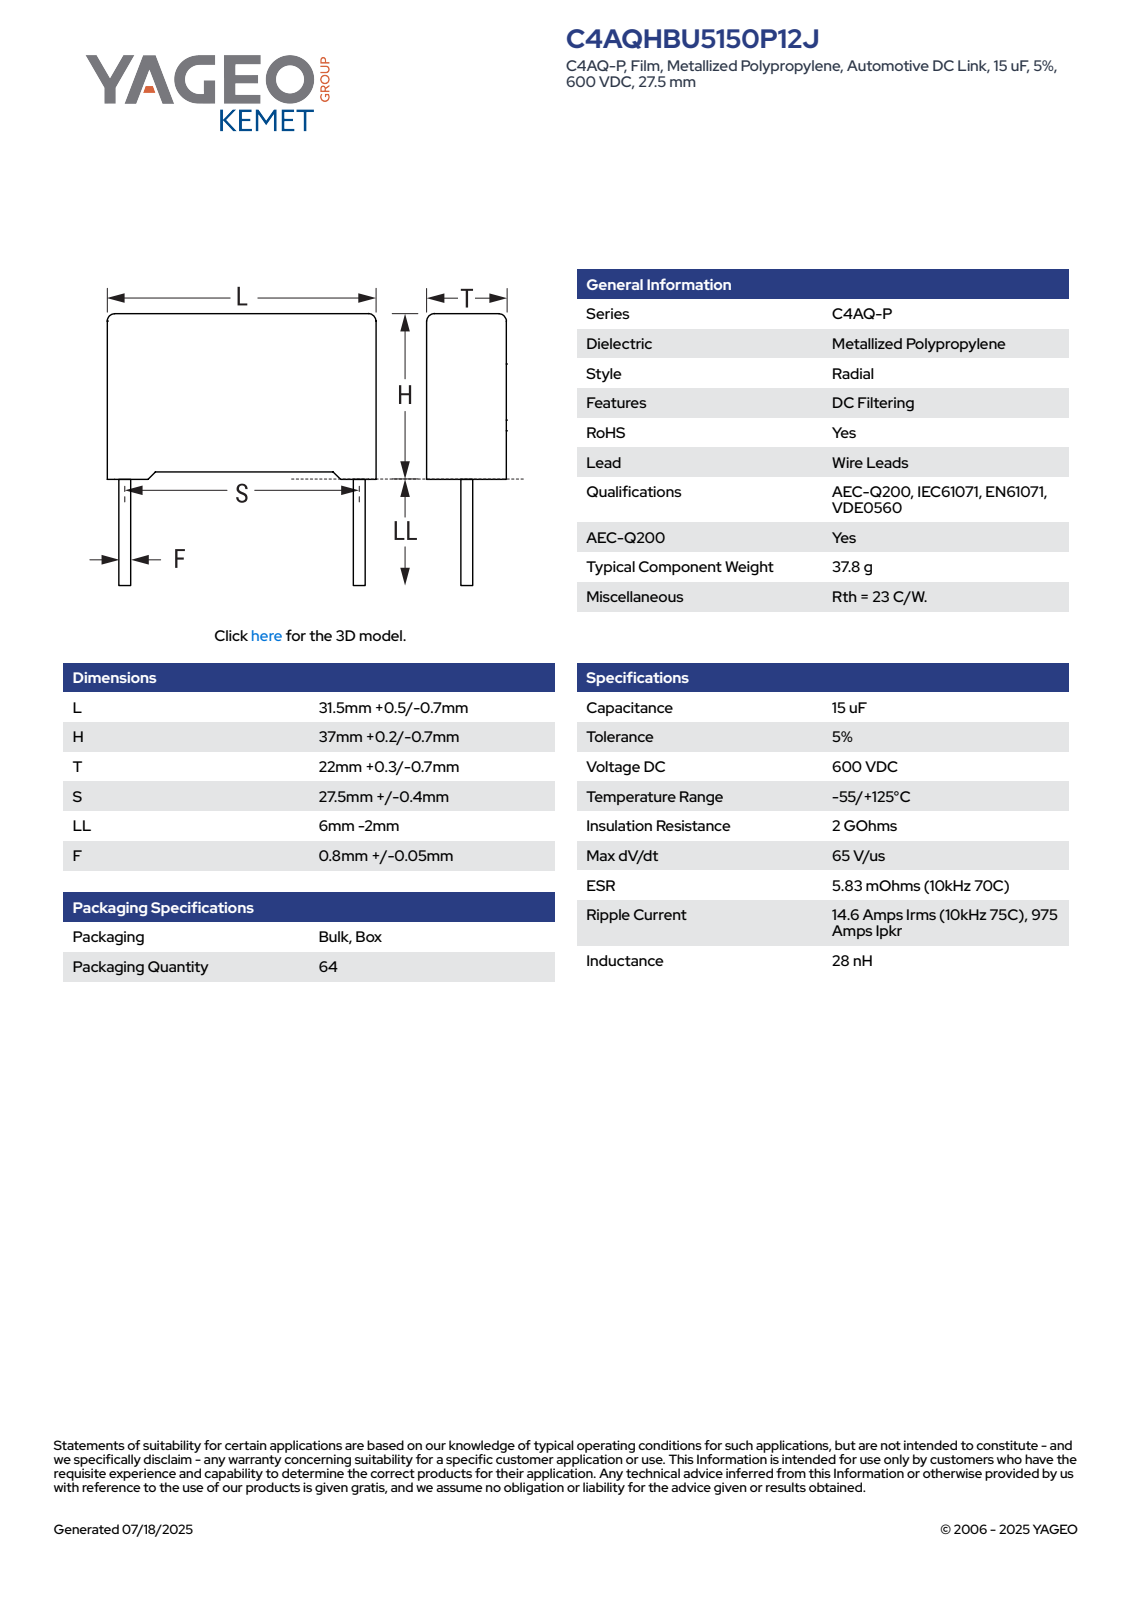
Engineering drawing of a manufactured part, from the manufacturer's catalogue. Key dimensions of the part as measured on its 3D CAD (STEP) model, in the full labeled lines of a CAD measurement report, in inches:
Part name (STEP PRODUCT): CFR_RB2CFP_31.5X37X22_L32H37.2T22.3S27.5LL4F0.85
STEP written by: SolidWorks 2014 (AUTOMOTIVE_DESIGN)
Units: inches
Bodies: 4 solids, 85 faces (77 planar, 8 cylindrical, 0 other)
Overall size (bounding box): 1.622 × 1.26 × 0.878
Volume: 1.573 in³ · Surface area: 8.584 in²
Round bosses / shafts (diameter × count): ⌀0.033 ×2
Partial cylindrical surfaces — rounded edges, fillets, slot ends (radius × count): R0.02 ×4
Main face-to-face distances: 0.878, 1.26, 1.414, 0.021, 1.435, 0.03, 0.05, 1.465, 0.042, 1.218
